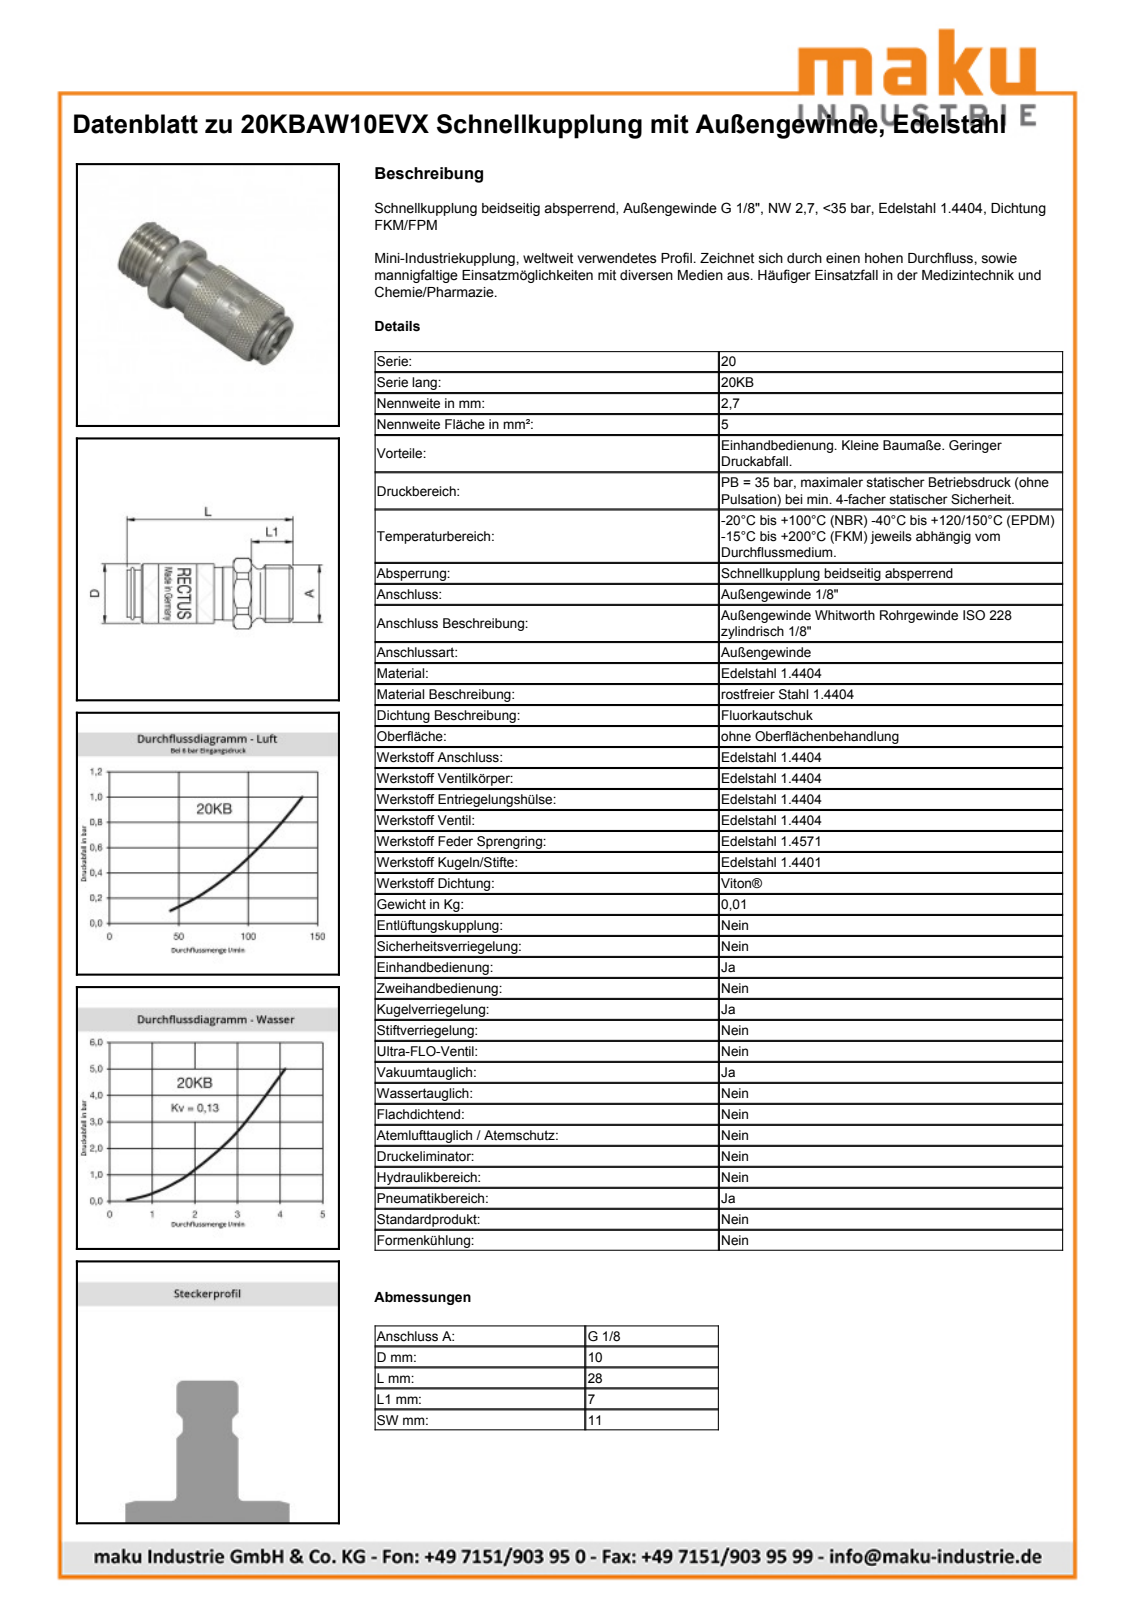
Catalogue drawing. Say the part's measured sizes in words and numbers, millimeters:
The part is named "D113102". Its 3-D file was written by "Autodesk Inventor 2013 (AUTOMOTIVE_DESIGN)". It is 2 solids with 439 faces: 145 planar, 68 cylindrical and 226 other. Overall it measures 28.05 by 12 by 11.13 millimeters. Its volume is 2 009 cubic millimeters and its surface area 1 931 square millimeters. Round holes: 1 of diameter 8.1, 1 of diameter 8.15, 1 of diameter 9.15, 1 of diameter 9.2. Round bosses or shafts: 1 of diameter 10.35, 1 of diameter 10, 1 of diameter 9.73, 1 of diameter 9, 1 of diameter 8, 1 of diameter 7.8, 1 of diameter 7.62. Partial cylindrical surfaces (rounded edges, fillets, slot ends): 1 of radius 4.9, 1 of radius 6. The main face-to-face distances are 28.05, 18, 10.05, 11, 3.3, 5, 2.4, 15.6, 25.65, 13.35.
